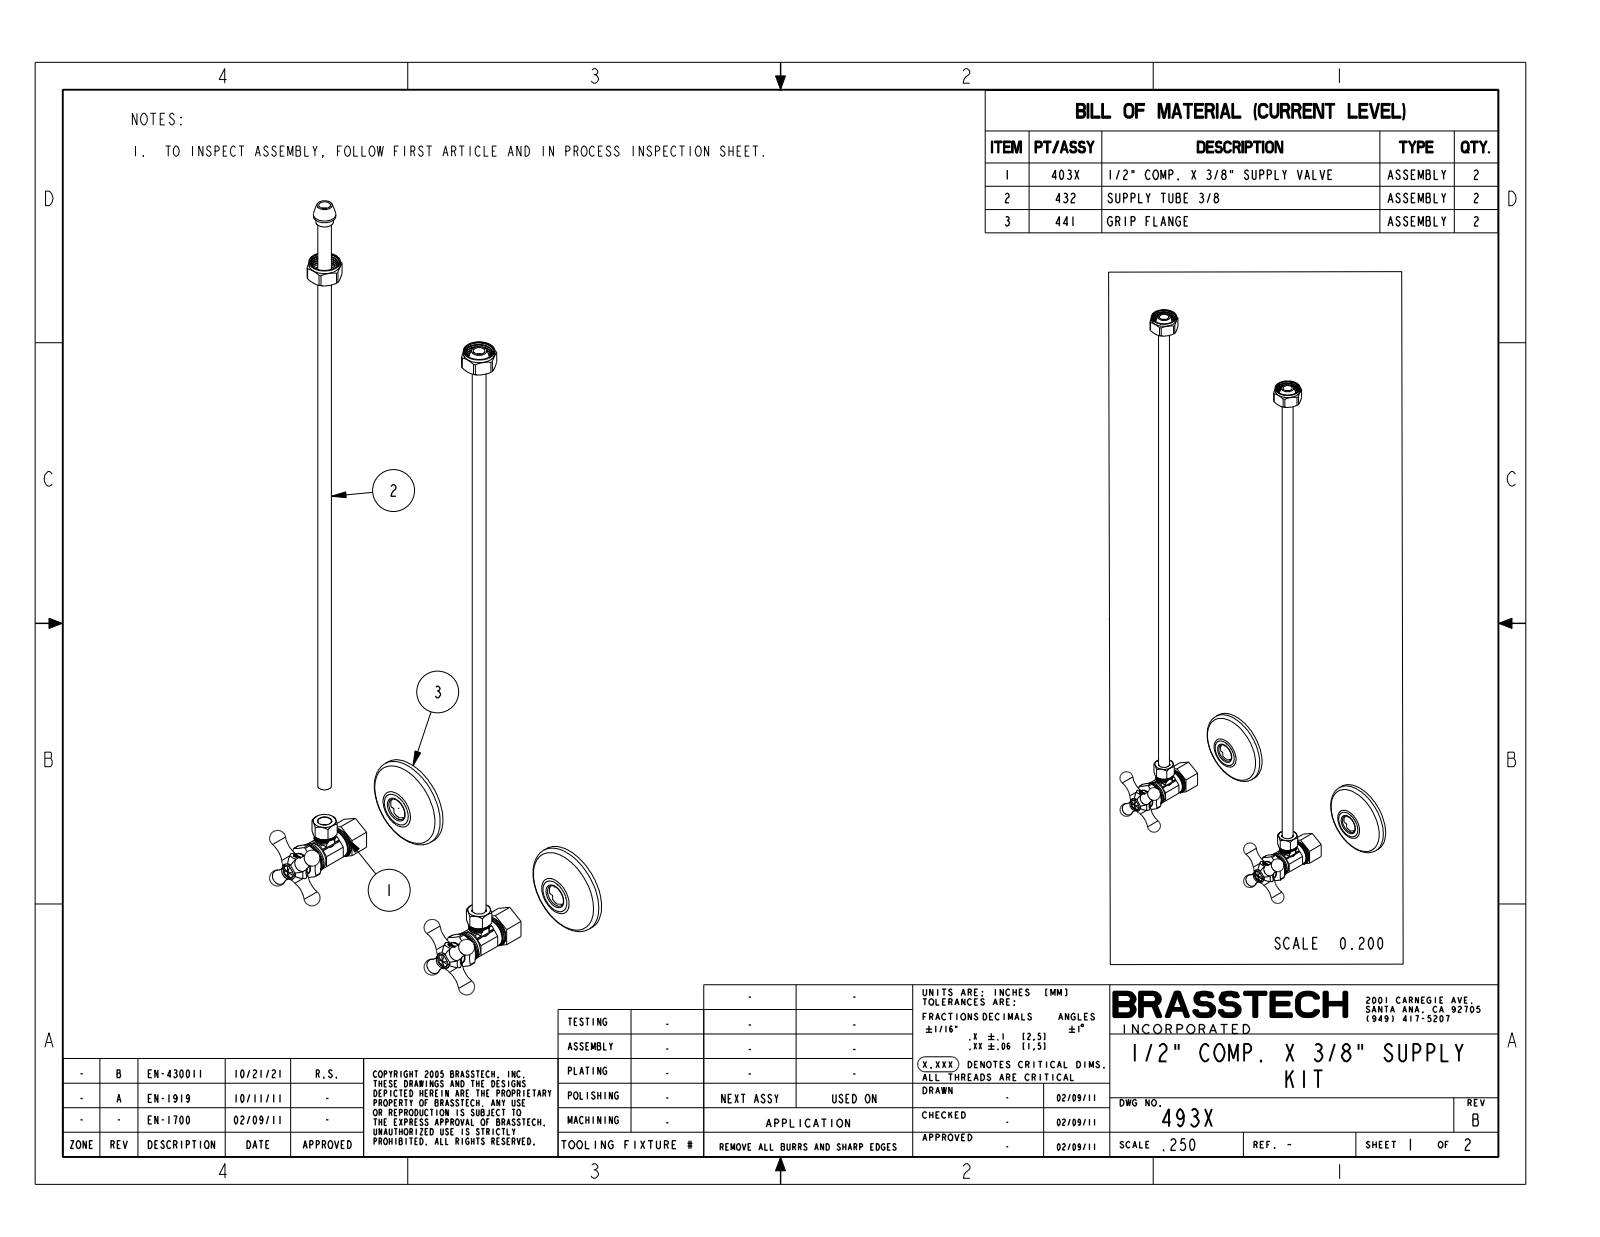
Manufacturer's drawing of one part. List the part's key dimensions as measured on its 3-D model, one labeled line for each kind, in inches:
Part name (STEP PRODUCT): 493X
STEP written by: CREO PARAMETRIC BY PTC INC, 2018500 (CONFIG_CONTROL_DESIGN)
Units: inches
Bodies: 9 solids, 1588 faces (412 planar, 581 cylindrical, 595 other)
Overall size (bounding box): 20.59 × 8.5 × 4.931
Volume: 2.274 in³ · Surface area: 255.6 in²
Round holes (diameter × count): ⌀0.13 ×2, ⌀0.32 ×2, ⌀0.375 ×2, ⌀0.377 ×2, ⌀0.38 ×2, ⌀0.392 ×2, ⌀0.4 ×2, ⌀0.464 ×2, ⌀0.48 ×2, ⌀0.515 ×2, ⌀0.517 ×2, ⌀0.52 ×2
Round bosses / shafts (diameter × count): ⌀2.5 ×2, ⌀0.867 ×2, ⌀0.86 ×2, ⌀0.753 ×2, ⌀0.68 ×2, ⌀0.677 ×2, ⌀0.665 ×2, ⌀0.655 ×2
Partial cylindrical surfaces — rounded edges, fillets, slot ends (radius × count): R0.01 ×36, R0.03 ×18, R0.05 ×12, R0.058 ×9, R0.17 ×2, R0.337 ×2, R0.376 ×2, R0.489 ×2
Main face-to-face distances: 0.875, 3, 6, 0.625, 0.125, 0.087, 5.196, 3.875, 2.125, 0.563
Hole centre spacings: 6, 1.09, 6.098
